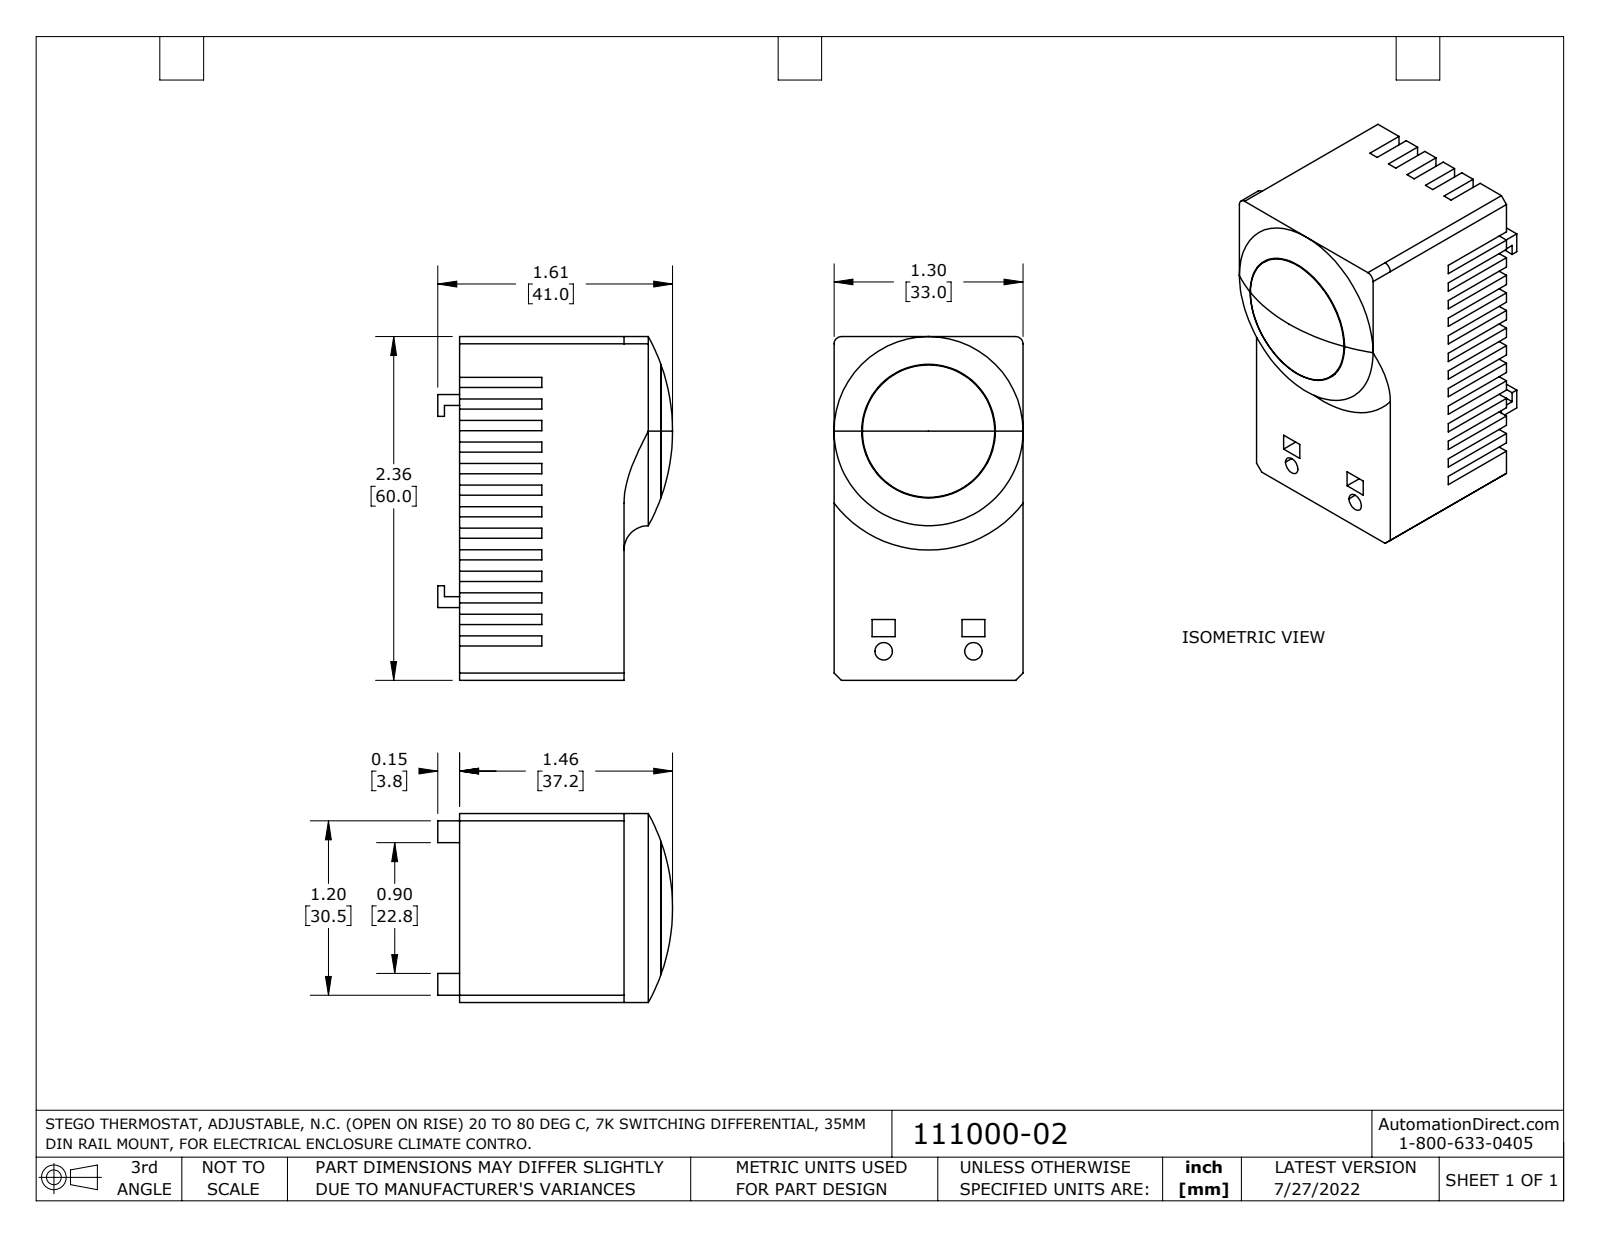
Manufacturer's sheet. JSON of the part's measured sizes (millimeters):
{"part_name": "111000-02_Default", "step_written_by": "SolidWorks 2021 (CONFIG_CONTROL_DESIGN)", "units": "millimeters", "bodies": {"solids": 1, "faces": 198, "planar": 183, "cylindrical": 10, "other": 5}, "overall_size": [60, 41, 33], "volume_mm3": 61240, "surface_area_mm2": 12850, "round_holes": [[3, 2], [23.3, 1]], "round_bosses_or_shafts": [[23.1, 1]], "partial_cylinders_radius": [[1.3, 2]], "face_to_face_distances": [33, 3.8, 1.8, 60, 7.5, 28.7, 11.3, 15, 2, 5.5], "hole_center_spacings": [39.2, 15.7]}
